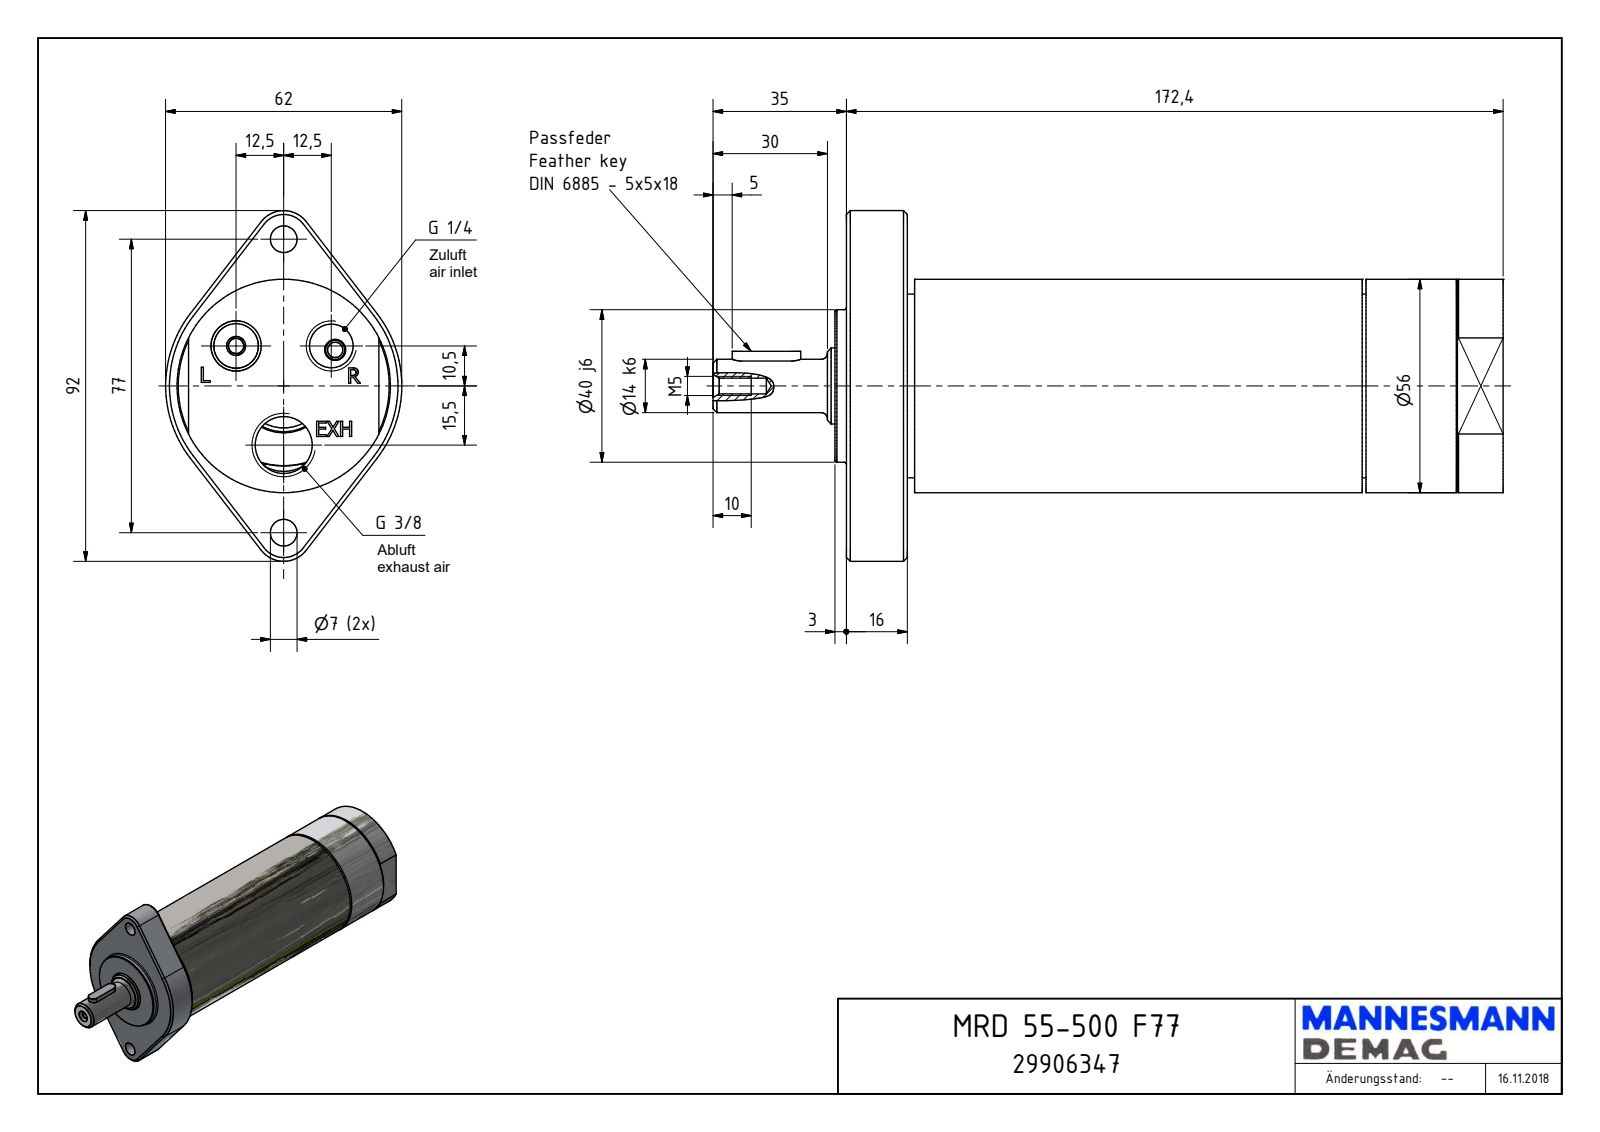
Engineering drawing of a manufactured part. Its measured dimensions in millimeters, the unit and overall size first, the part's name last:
Units: millimetres
Overall size (bounding box): 207.4 × 92 × 62
Round holes (diameter × count): ⌀7 ×2, ⌀4 ×1, ⌀4.13 ×1, ⌀11.45 ×1, ⌀14.95 ×1, ⌀21 ×1
Round bosses / shafts (diameter × count): ⌀56 ×1, ⌀51.99 ×1, ⌀40 ×1, ⌀19.95 ×1, ⌀14 ×1
Partial cylindrical surfaces — rounded edges, fillets, slot ends (radius × count): R2.5 ×2, R7.5 ×2, R31 ×1
Main face-to-face distances: 172.4, 16, 156.4, 3, 19, 175.4, 61.98, 61.96, 138.4, 135.4
Hole centre spacings: 16.32, 28.85, 30.66, 38.5, 50.57, 15.5, 23, 25
Volume: 447 490 mm³ · Surface area: 43 151 mm²
Bodies: 1 solid, 157 faces (104 planar, 22 cylindrical, 31 other)
Part name (STEP PRODUCT): MRD 55-500 F77_29906347
STEP written by: Autodesk Inventor 2024 (AUTOMOTIVE_DESIGN)
